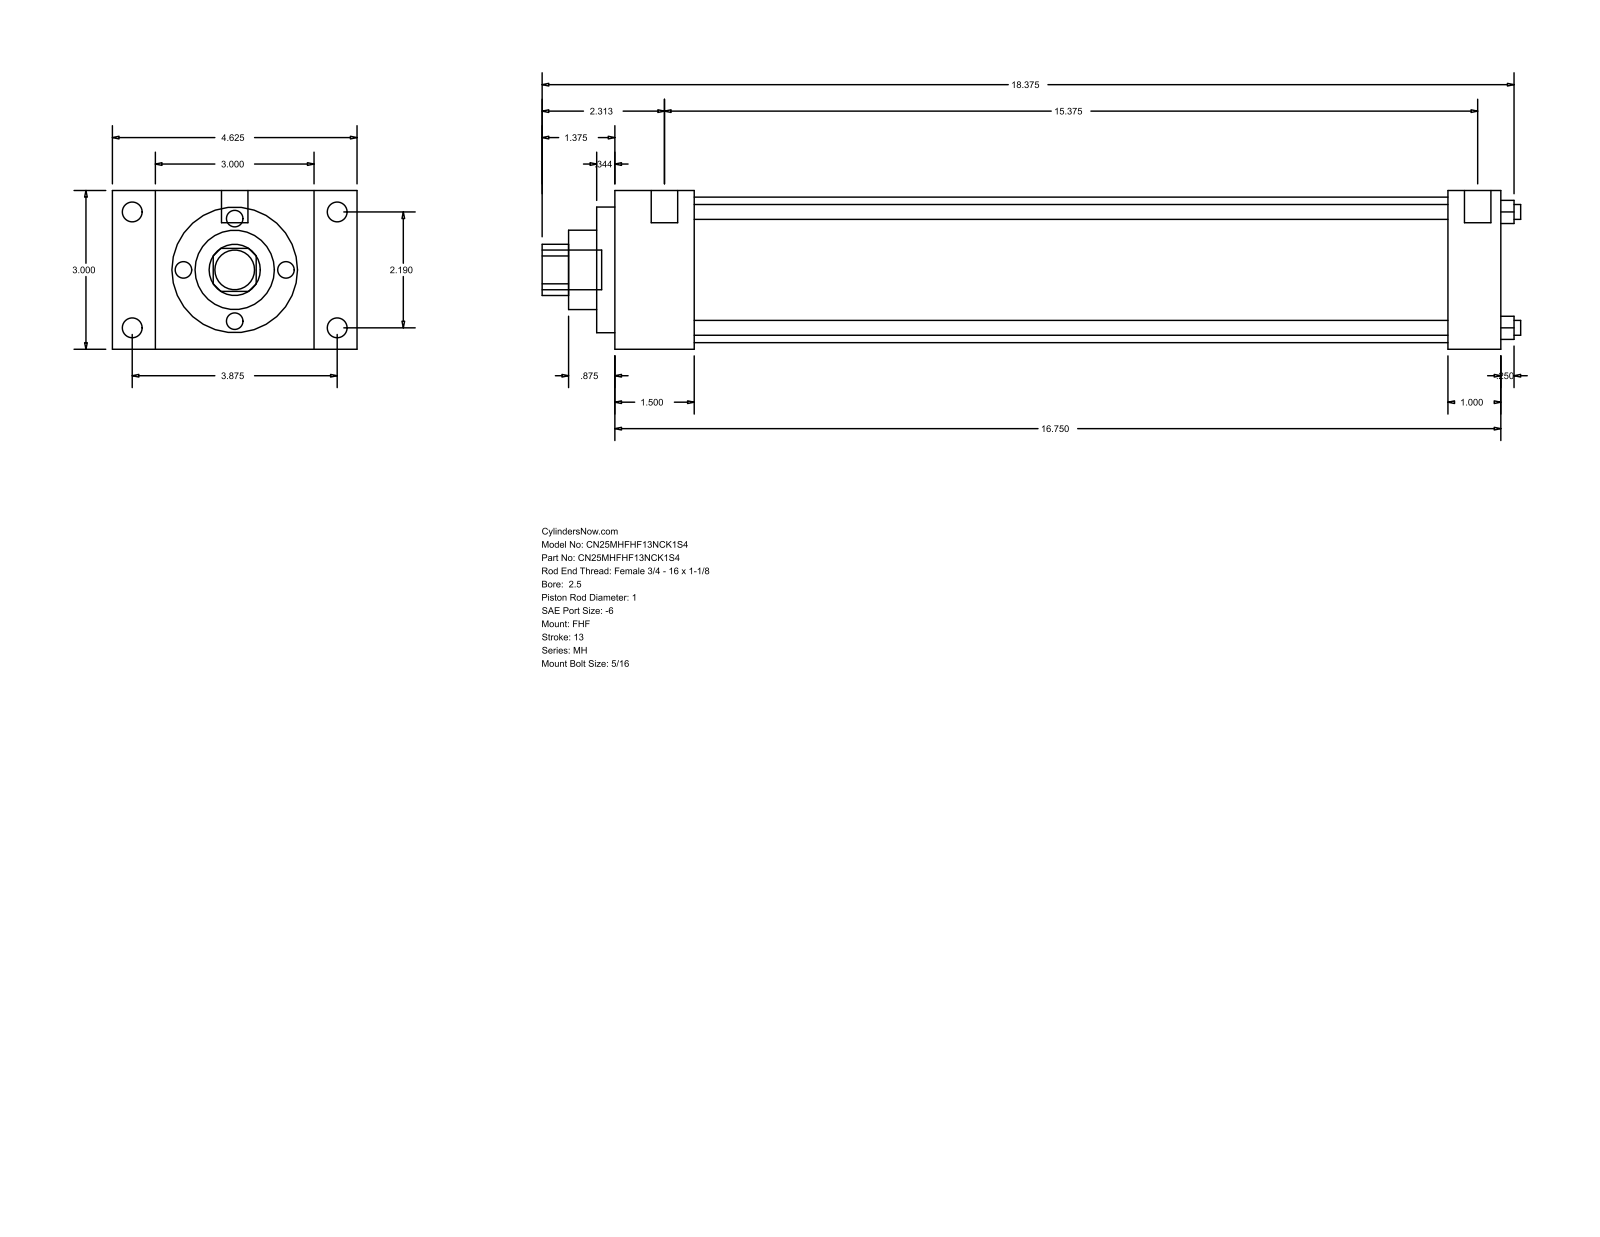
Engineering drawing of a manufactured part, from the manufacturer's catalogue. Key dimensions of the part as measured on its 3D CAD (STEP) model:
Part name (STEP PRODUCT): MH_FHF__0250_1
STEP written by: GSSL Pune (CONFIG_CONTROL_DESIGN)
Units: millimetres
Bodies: 0 solids, 90 faces (61 planar, 29 cylindrical, 0 other)
Overall size (bounding box): 469.9 × 117.47 × 76.2
Round holes (diameter × count): ⌀7.14 ×4, ⌀25.4 ×1, ⌀38.1 ×1, ⌀60.33 ×1, ⌀69.85 ×1
Round bosses / shafts (diameter × count): ⌀9.53 ×4, ⌀5.56 ×4, ⌀12.7 ×2, ⌀19.05 ×1
Partial cylindrical surfaces — rounded edges, fillets, slot ends (radius × count): R12.29 ×1
Main face-to-face distances: 76.2, 425.46, 38.11, 387.35, 20.64, 96.84, 117.48, 400.06, 361.95, 25.4
Hole centre spacings: 39.33, 55.62, 78.66
